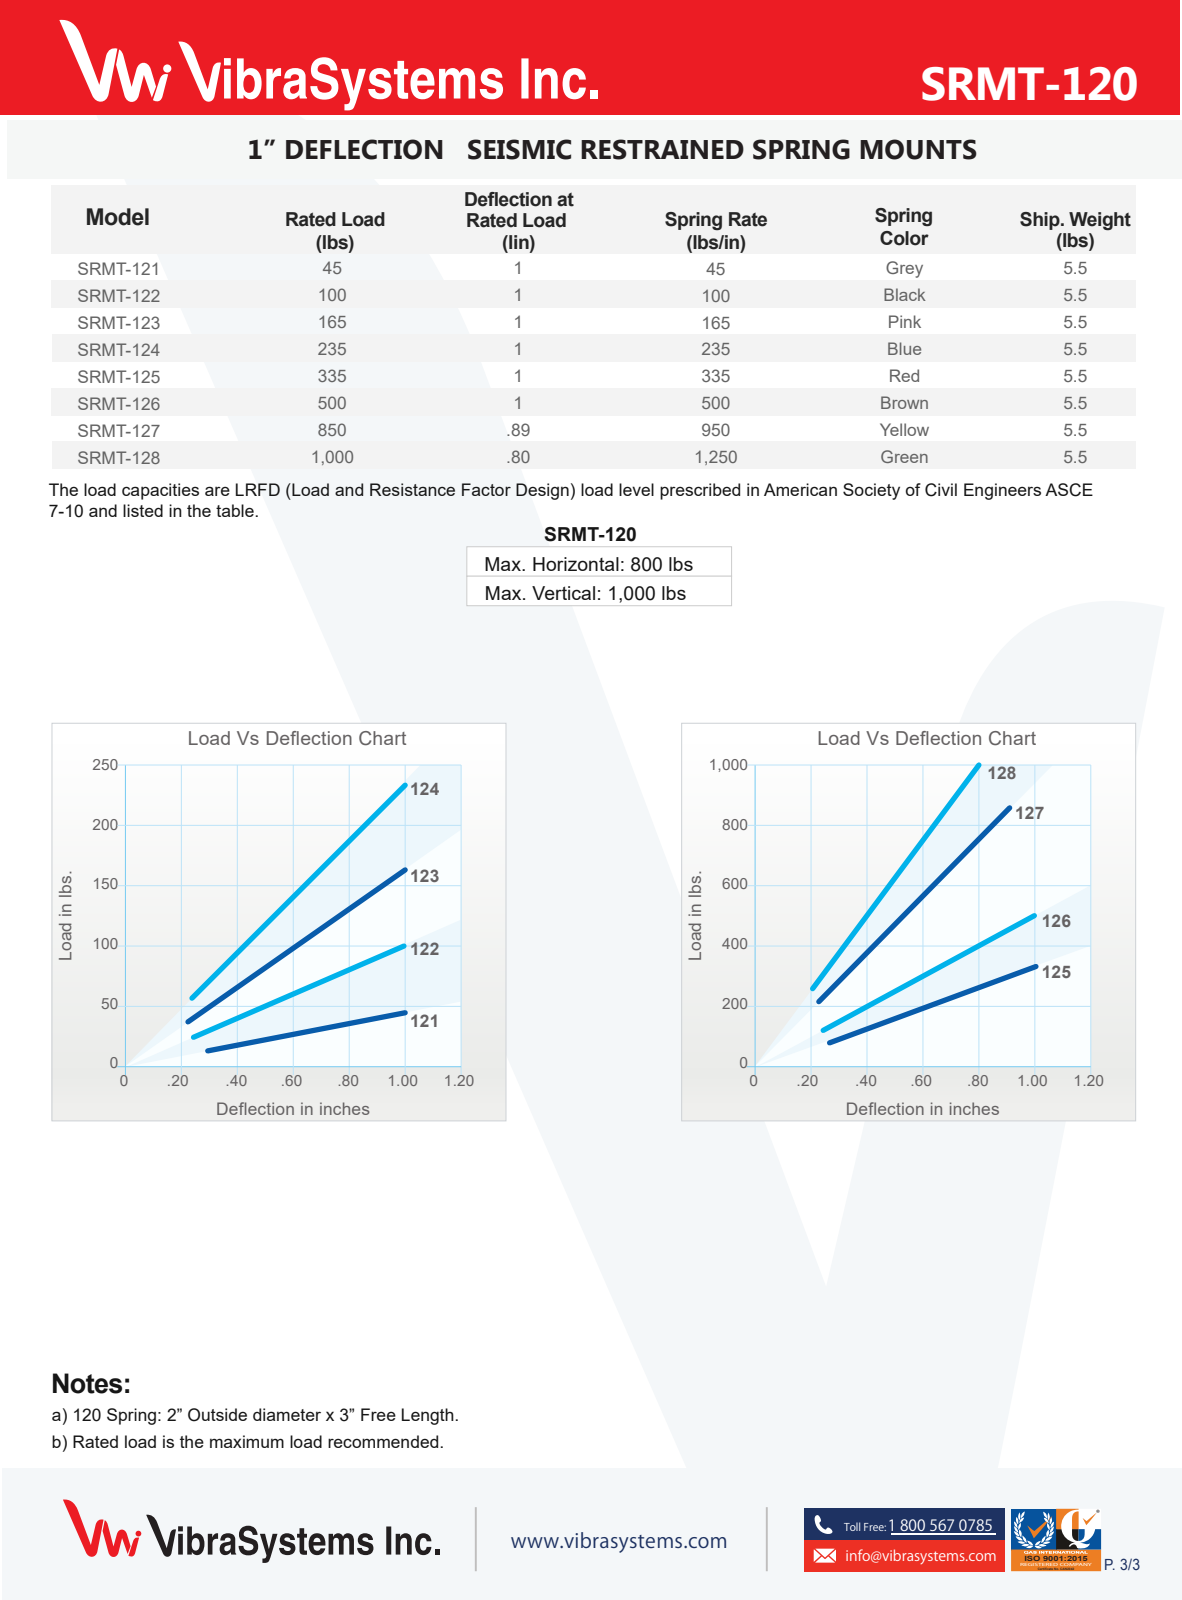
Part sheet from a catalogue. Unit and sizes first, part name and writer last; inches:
Units: inches
Overall size (bounding box): 5.5 × 4.5 × 2
Round holes (diameter × count): ⌀0.437 ×2, ⌀0.625 ×1
Round bosses / shafts (diameter × count): ⌀0.59 ×2, ⌀1.574 ×1, ⌀1.25 ×1, ⌀1 ×1, ⌀0.75 ×1, ⌀0.375 ×1
Partial cylindrical surfaces — rounded edges, fillets, slot ends (radius × count): R0.25 ×12, R0.167 ×4, R0.5 ×4
Main face-to-face distances: 0.083, 1.917, 2, 1.834, 0.25, 2.435, 2.185, 2.248, 1.998, 0.187
Hole centre spacings: 1.75, 3.5
Volume: 8.921 in³ · Surface area: 79.76 in²
Bodies: 1 solid, 114 faces (70 planar, 44 cylindrical, 0 other)
Part name (STEP PRODUCT): SRMT-020 Rev K
STEP written by: SolidWorks 2016 (CONFIG_CONTROL_DESIGN)
